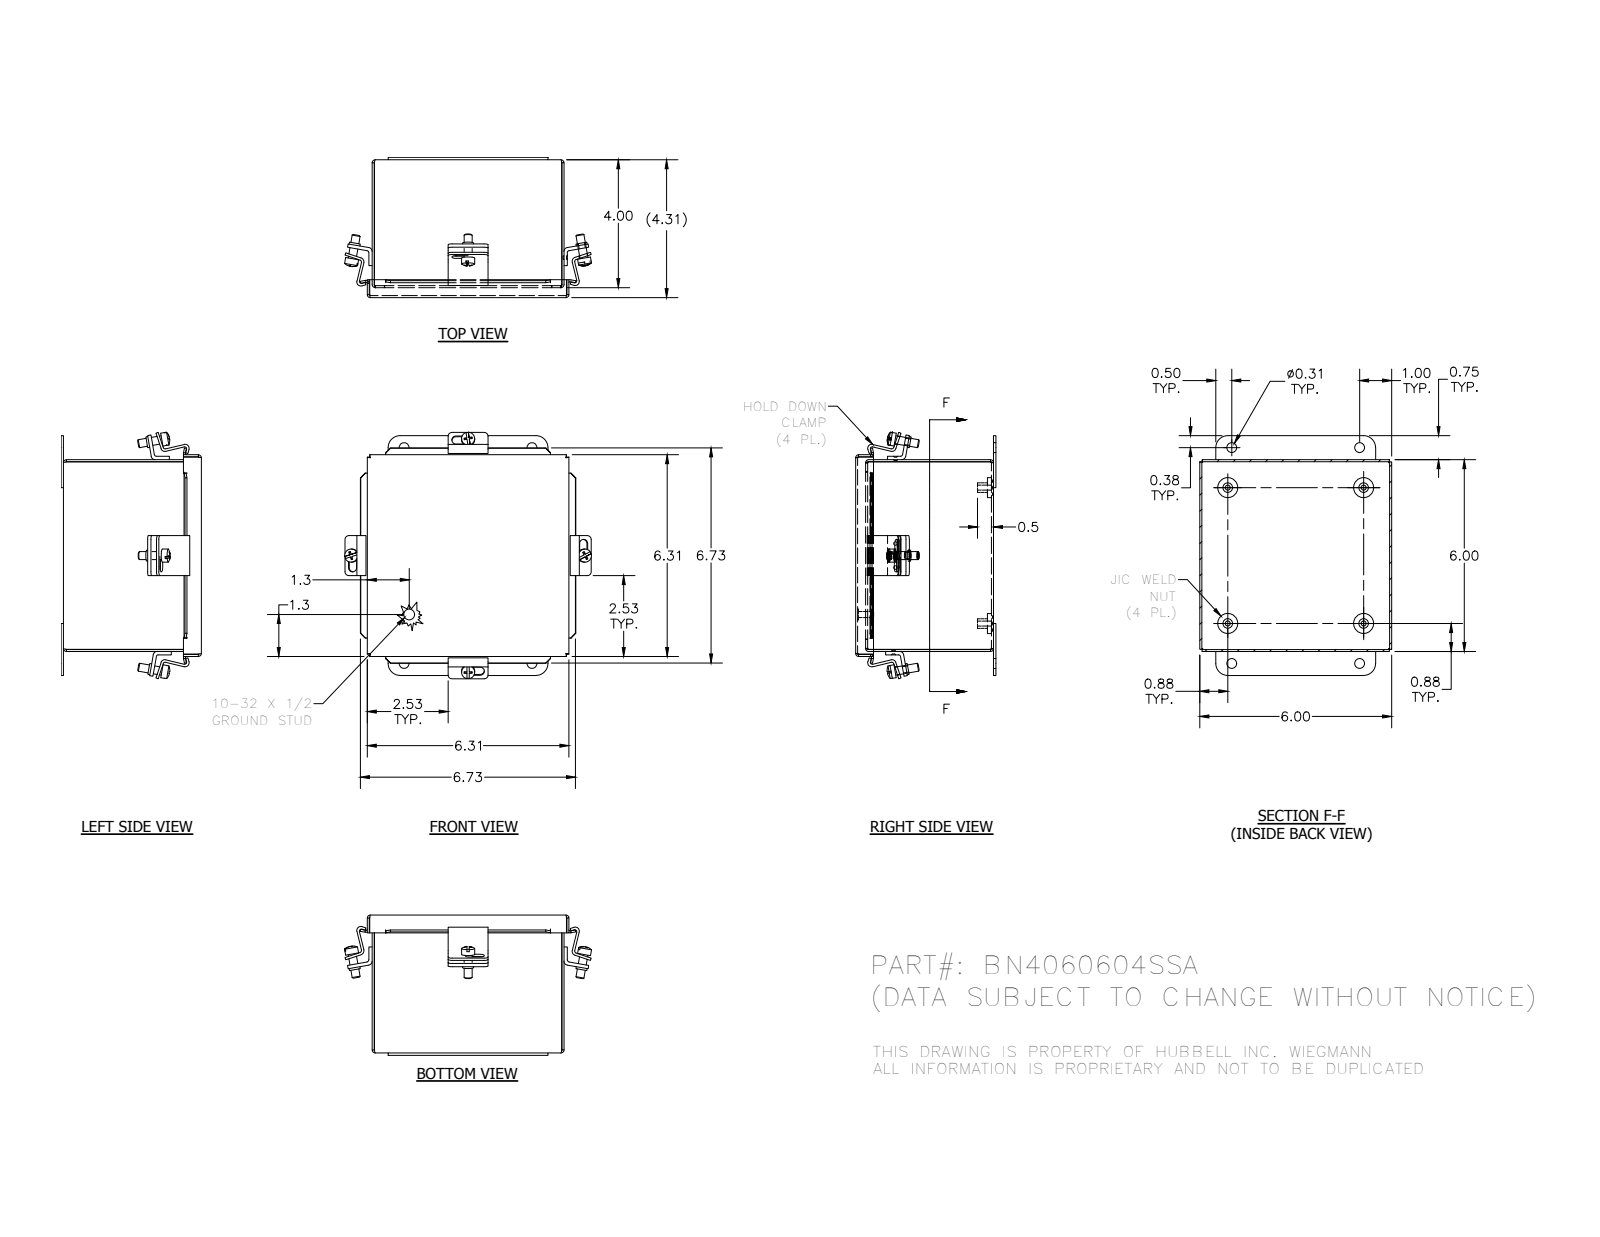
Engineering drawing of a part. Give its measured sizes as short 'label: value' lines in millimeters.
name: 30810_1; BN4060604SSABKP_1; 34973_1; 372164_1 (+5 more)
written by: SolidWorks 2014 (AUTOMOTIVE_DESIGN)
unit: mm
bodies: 21 solids, 589 faces (287 planar, 200 cylindrical, 102 other)
size: 196.2 × 195.9 × 111.5
volume: 240 200 mm³; area: 296 100 mm²
holes: 6× ⌀2.8, 4× ⌀4, 4× ⌀5, 4× ⌀7.9
bosses: 4× ⌀15.9, 4× ⌀10.4, 4× ⌀8.7, 4× ⌀7.6, 4× ⌀6.4, 1× ⌀8.6, 1× ⌀4.8
rounds: 16× R0.8, 16× R2.4, 16× R3.2, 12× R1.6, 12× R3.2, 8× R3.4, 4× R9.5
face distances: 1.6, 150.8, 108, 152.4, 149.2, 109.6, 106.3, 1.9, 3.9, 154.8
hole spacings: 31.9, 108, 109.5, 139.8, 19.1, 1.6, 19.1, 101.6
